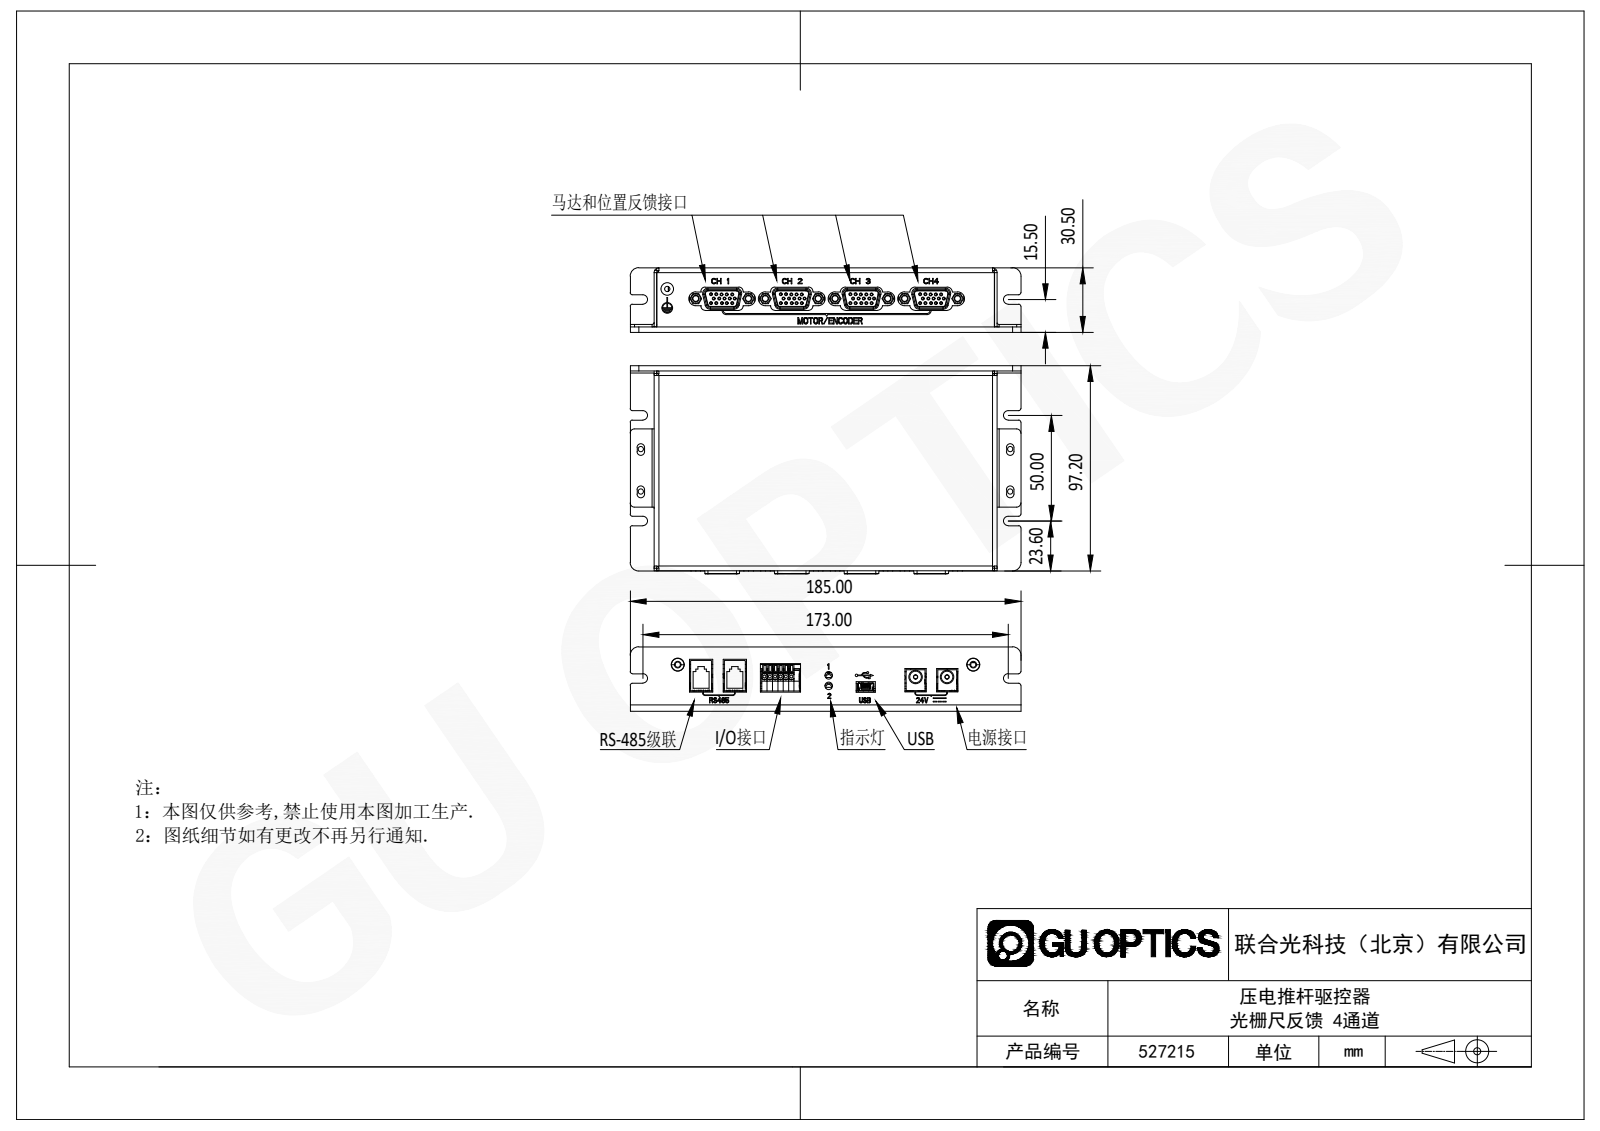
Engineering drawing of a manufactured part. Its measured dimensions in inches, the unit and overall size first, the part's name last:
Units: inches
Overall size (bounding box): 7.283 × 3.882 × 1.201
Round holes (diameter × count): ⌀0.012 ×254, ⌀0.039 ×104, ⌀0.047 ×15, ⌀0.098 ×13, ⌀0.035 ×10, ⌀0.102 ×8, ⌀0.128 ×8, ⌀0.161 ×8, ⌀0.043 ×6, ⌀0.059 ×6, ⌀0.118 ×5, ⌀0.018 ×4
Round bosses / shafts (diameter × count): ⌀0.026 ×36, ⌀0.157 ×8, ⌀0.056 ×8, ⌀0.035 ×8, ⌀0.212 ×6, ⌀0.051 ×6, ⌀0.09 ×4, ⌀0.077 ×4
Partial cylindrical surfaces — rounded edges, fillets, slot ends (radius × count): R0.008 ×58, R0.004 ×44, R0.02 ×38, R0.074 ×32, R0.039 ×30, R0.059 ×24, R0.01 ×16, R0.071 ×16
Main face-to-face distances: 0.047, 0.098, 1.055, 1.102, 1.201, 1.154, 0.823, 0.378, 0.279, 0.776
Hole centre spacings: 0.098, 0.039, 0.295, 0.161, 0.189, 0.196, 1.299, 2.411
Volume: 7.821 in³ · Surface area: 235.7 in²
Bodies: 49 solids, 7649 faces (4542 planar, 1868 cylindrical, 1239 other)
Part name (STEP PRODUCT): 5272133
STEP written by: SolidWorks 2020 (CONFIG_CONTROL_DESIGN)
